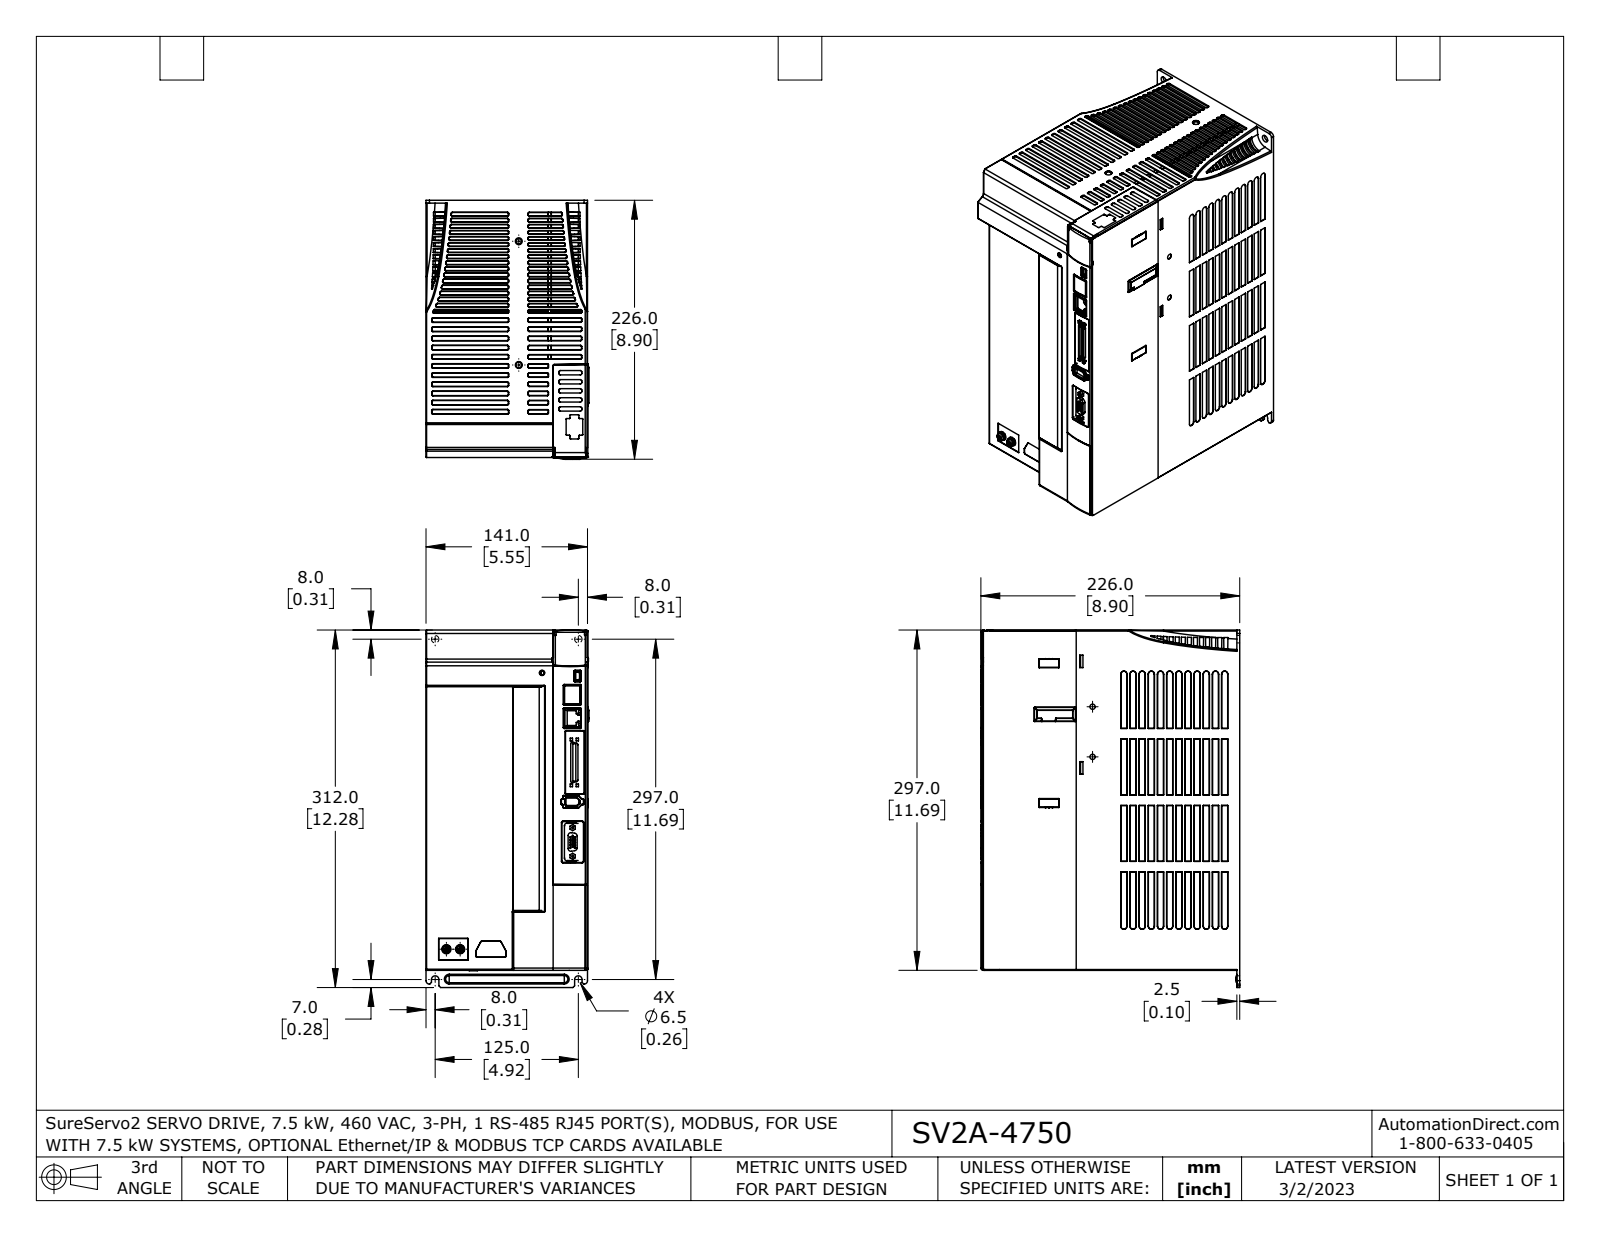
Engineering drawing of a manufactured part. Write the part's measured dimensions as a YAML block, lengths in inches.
part_name: "SV2A-4750_3D_All_20200930 1st B3c Extcoord NEW2Cm1Cb coord"
step_written_by: "SolidWorks 2021 (AUTOMOTIVE_DESIGN)"
units: inches
bodies: {solids: 1, faces: 2555, planar: 1190, cylindrical: 498, other: 867}
overall_size: [12.283, 8.902, 5.591]
volume: 549
surface_area: 500.7
round_holes:
  - {diameter: 0.044, count: 15}
  - {diameter: 0.067, count: 2}
  - {diameter: 0.114, count: 2}
  - {diameter: 0.118, count: 2}
  - {diameter: 0.236, count: 2}
  - {diameter: 0.256, count: 2}
round_bosses_or_shafts:
  - {diameter: 0.315, count: 2}
  - {diameter: 0.276, count: 2}
  - {diameter: 0.256, count: 2}
  - {diameter: 0.157, count: 2}
partial_cylinders:
  - {radius: 0.012, count: 82}
  - {radius: 0.02, count: 81}
  - {radius: 0.004, count: 27}
  - {radius: 0.059, count: 10}
  - {radius: 0.098, count: 7}
  - {radius: 0.01, count: 6}
  - {radius: 0.017, count: 6}
  - {radius: 0.028, count: 6}
face_to_face_distances: [5.55, 5.561, 5.56, 5.549, 5.551, 8.276, 11.693, 11.692, 0.02, 11.689]
hole_center_spacings: [0.09, 0.156, 0.238, 0.09, 0.18, 0.18, 0.156, 0.27]
